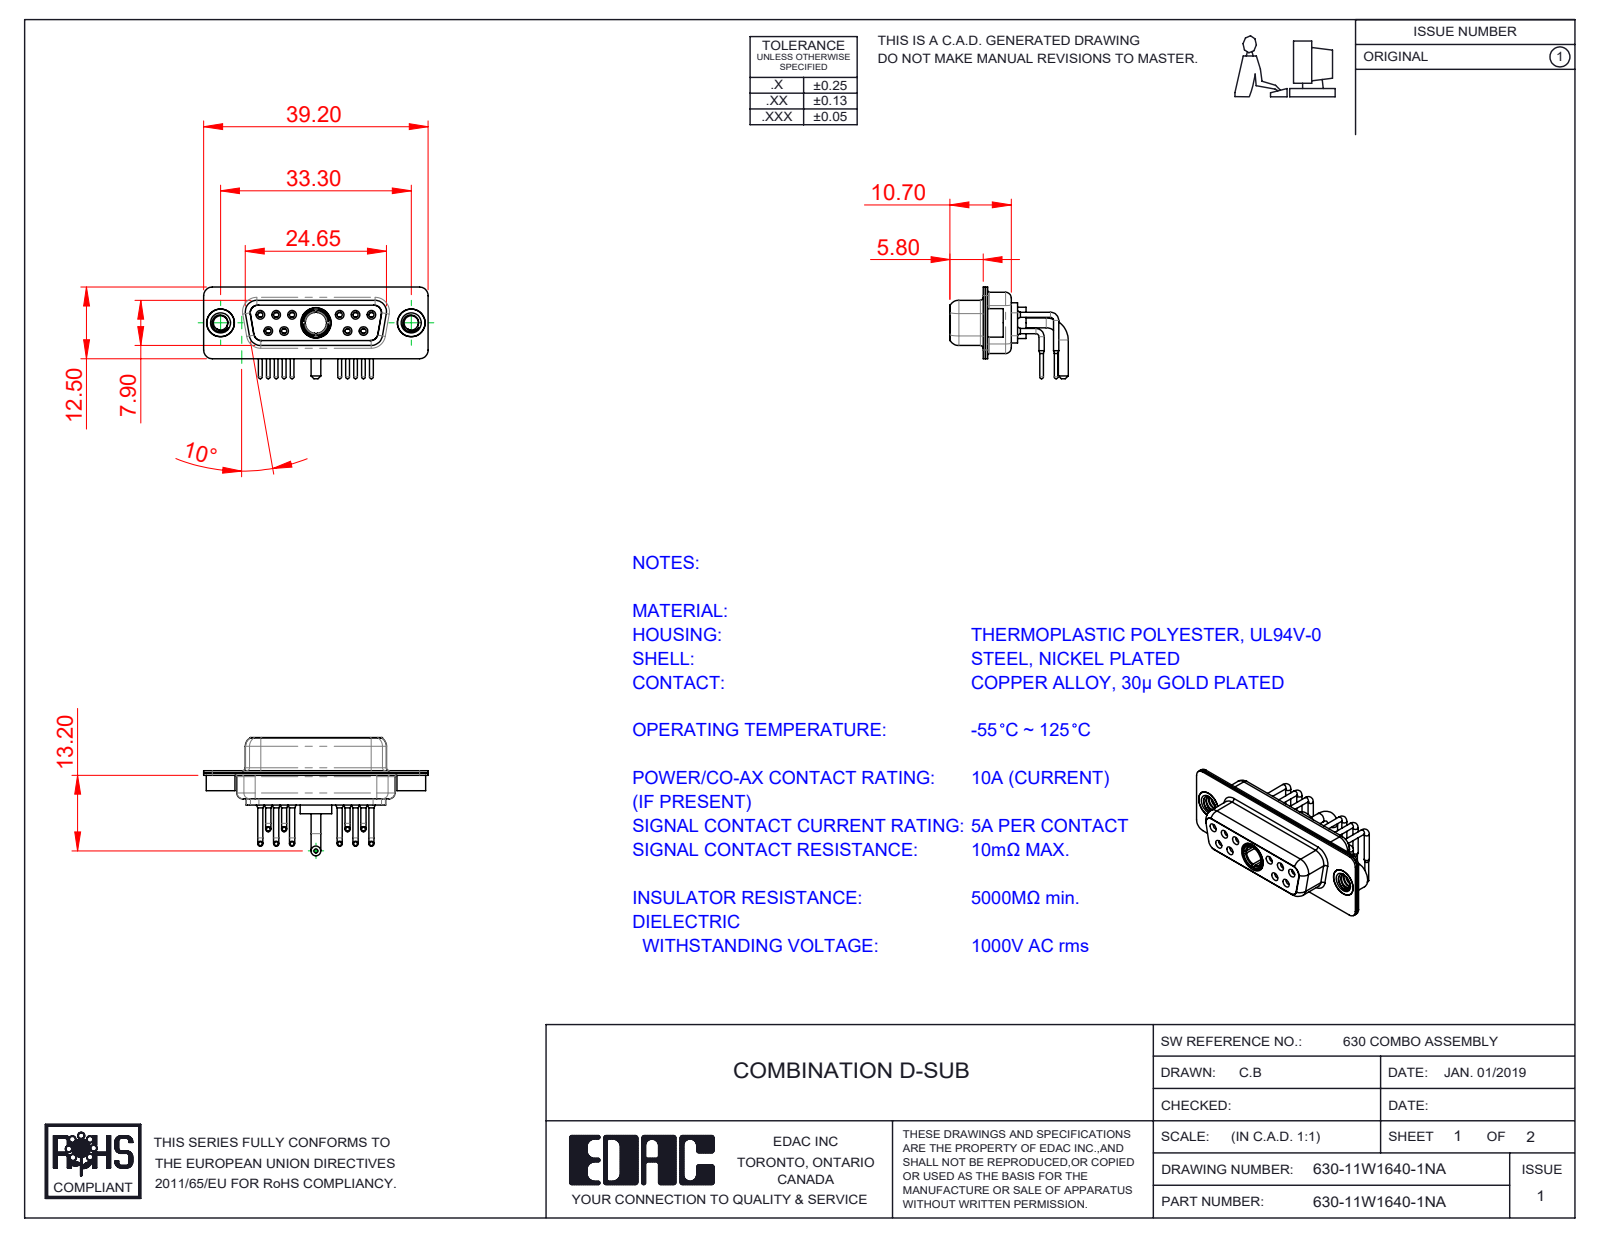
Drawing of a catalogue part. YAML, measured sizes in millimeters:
part_name: "630Combo Threaded Rivet_A; 630Combo Shell Front_15 Contacts; 630Combo Housing_11W1; 630-11W1640-1NA (+4 more)"
step_written_by: "SolidWorks 2020 (CONFIG_CONTROL_DESIGN)"
units: millimeters
bodies: {solids: 17, faces: 881, planar: 246, cylindrical: 390, other: 245}
overall_size: [39.2, 20.65, 16]
volume: 2582
surface_area: 6225
round_holes:
  - {diameter: 0.9, count: 10}
  - {diameter: 1.1, count: 10}
  - {diameter: 1.5, count: 10}
  - {diameter: 2, count: 10}
  - {diameter: 1.7, count: 6}
  - {diameter: 1.6, count: 4}
  - {diameter: 4.85, count: 3}
  - {diameter: 2.5, count: 2}
  - {diameter: 4, count: 2}
  - {diameter: 4.05, count: 2}
  - {diameter: 3.7, count: 1}
  - {diameter: 5.3, count: 1}
round_bosses_or_shafts:
  - {diameter: 0.9, count: 10}
  - {diameter: 0.65, count: 10}
  - {diameter: 1.6, count: 6}
  - {diameter: 5, count: 2}
  - {diameter: 4.95, count: 2}
  - {diameter: 4.8, count: 2}
  - {diameter: 1.7, count: 2}
  - {diameter: 5.5, count: 1}
partial_cylinders:
  - {radius: 1.5, count: 16}
  - {radius: 1.35, count: 12}
  - {radius: 2, count: 12}
  - {radius: 1.6, count: 8}
  - {radius: 0.25, count: 4}
  - {radius: 0.5, count: 4}
  - {radius: 0.6, count: 4}
  - {radius: 0.65, count: 4}
face_to_face_distances: [0.4, 1.4, 0.45, 8.45, 1.8, 8.9, 0.8, 6.2, 7.05, 1.85]
hole_center_spacings: [3.16, 2.77, 13.85, 11.08, 16.62, 5.03, 5.04, 5.54]
